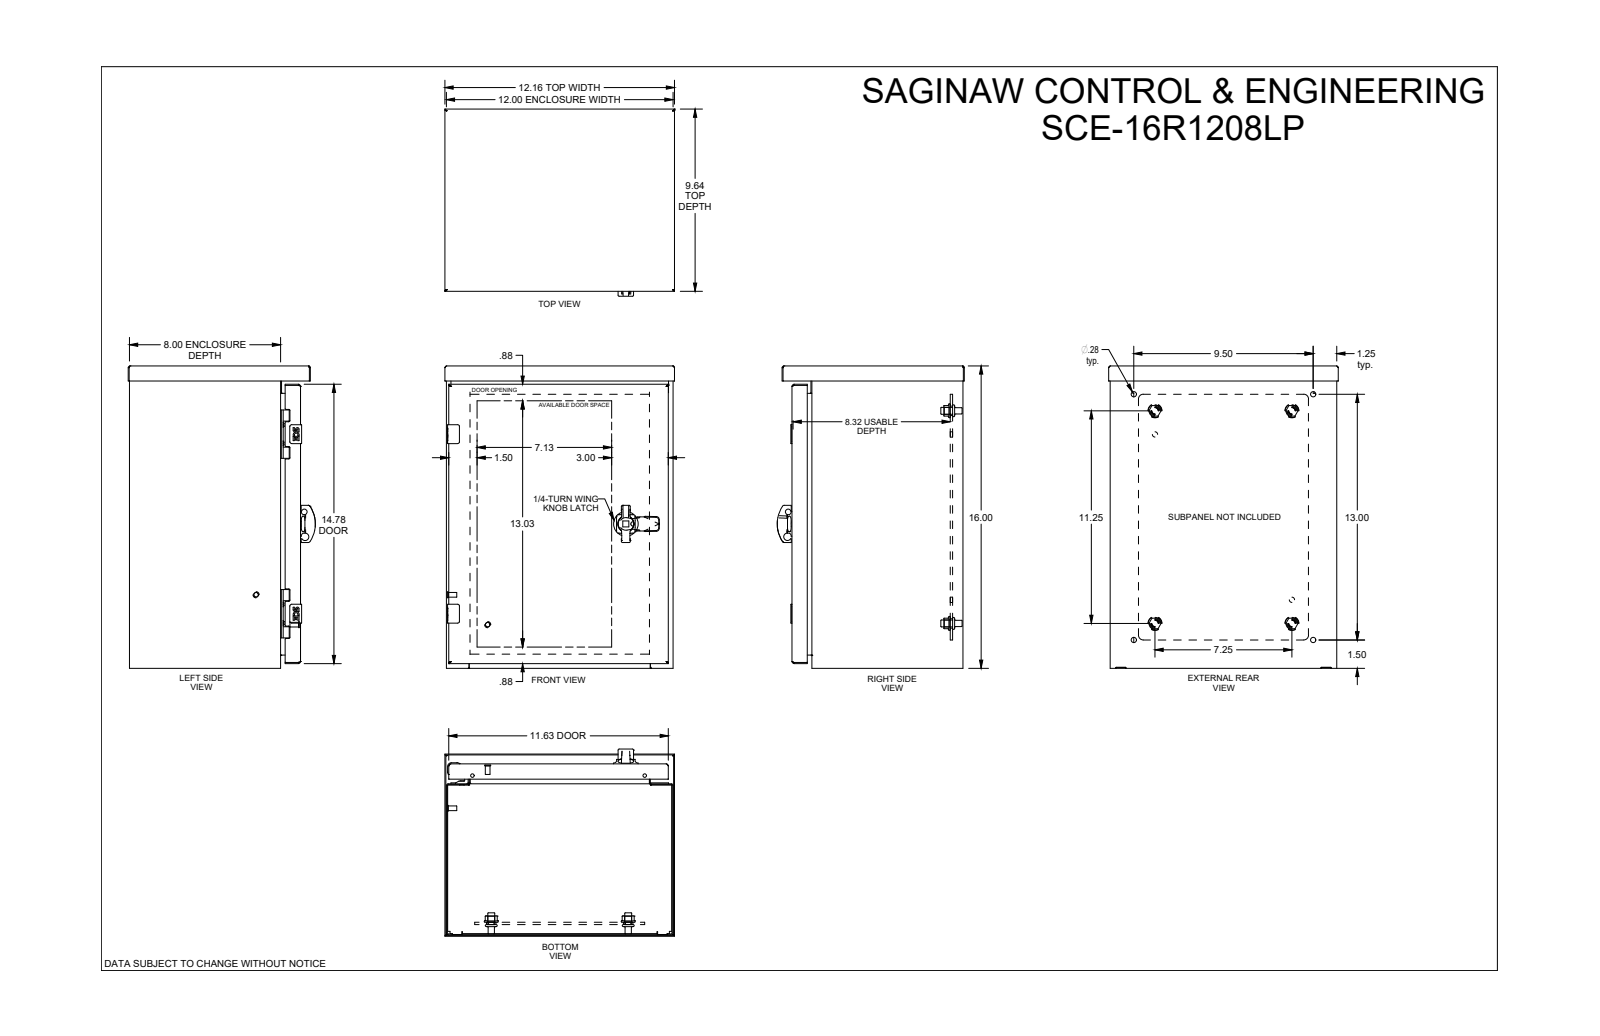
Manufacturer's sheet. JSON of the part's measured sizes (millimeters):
{"part_name": "SCE-16R1208LP_REV2", "step_written_by": "SolidWorks 2021 (AUTOMOTIVE_DESIGN)", "units": "millimeters", "bodies": {"solids": 23, "faces": 1201, "planar": 549, "cylindrical": 469, "other": 183}, "overall_size": [406.4, 308.8, 252.7], "volume_mm3": 1407000, "surface_area_mm2": 1556000, "round_holes": [[4.4, 4], [5.2, 4], [6.2, 4], [6.8, 4], [7.1, 4], [9.5, 4], [12.7, 4], [1, 2], [4.8, 2], [5.5, 2], [7.1, 2], [5.2, 1]], "round_bosses_or_shafts": [[9.3, 4], [8.4, 4], [6.4, 4], [6.1, 4], [6.3, 2], [33.1, 1], [22, 1], [20.8, 1]], "partial_cylinders_radius": [[0.4, 36], [1.5, 25], [1.6, 12], [0.8, 10], [1.6, 8], [2.5, 8], [5.6, 8], [0.8, 6]], "face_to_face_distances": [1.5, 228.4, 303.3, 226.9, 404.9, 229.9, 304.8, 301.8, 13.9, 12.4], "hole_center_spacings": [241.3, 12.5, 12.5, 25, 25, 152.4, 184.2, 186.9]}
